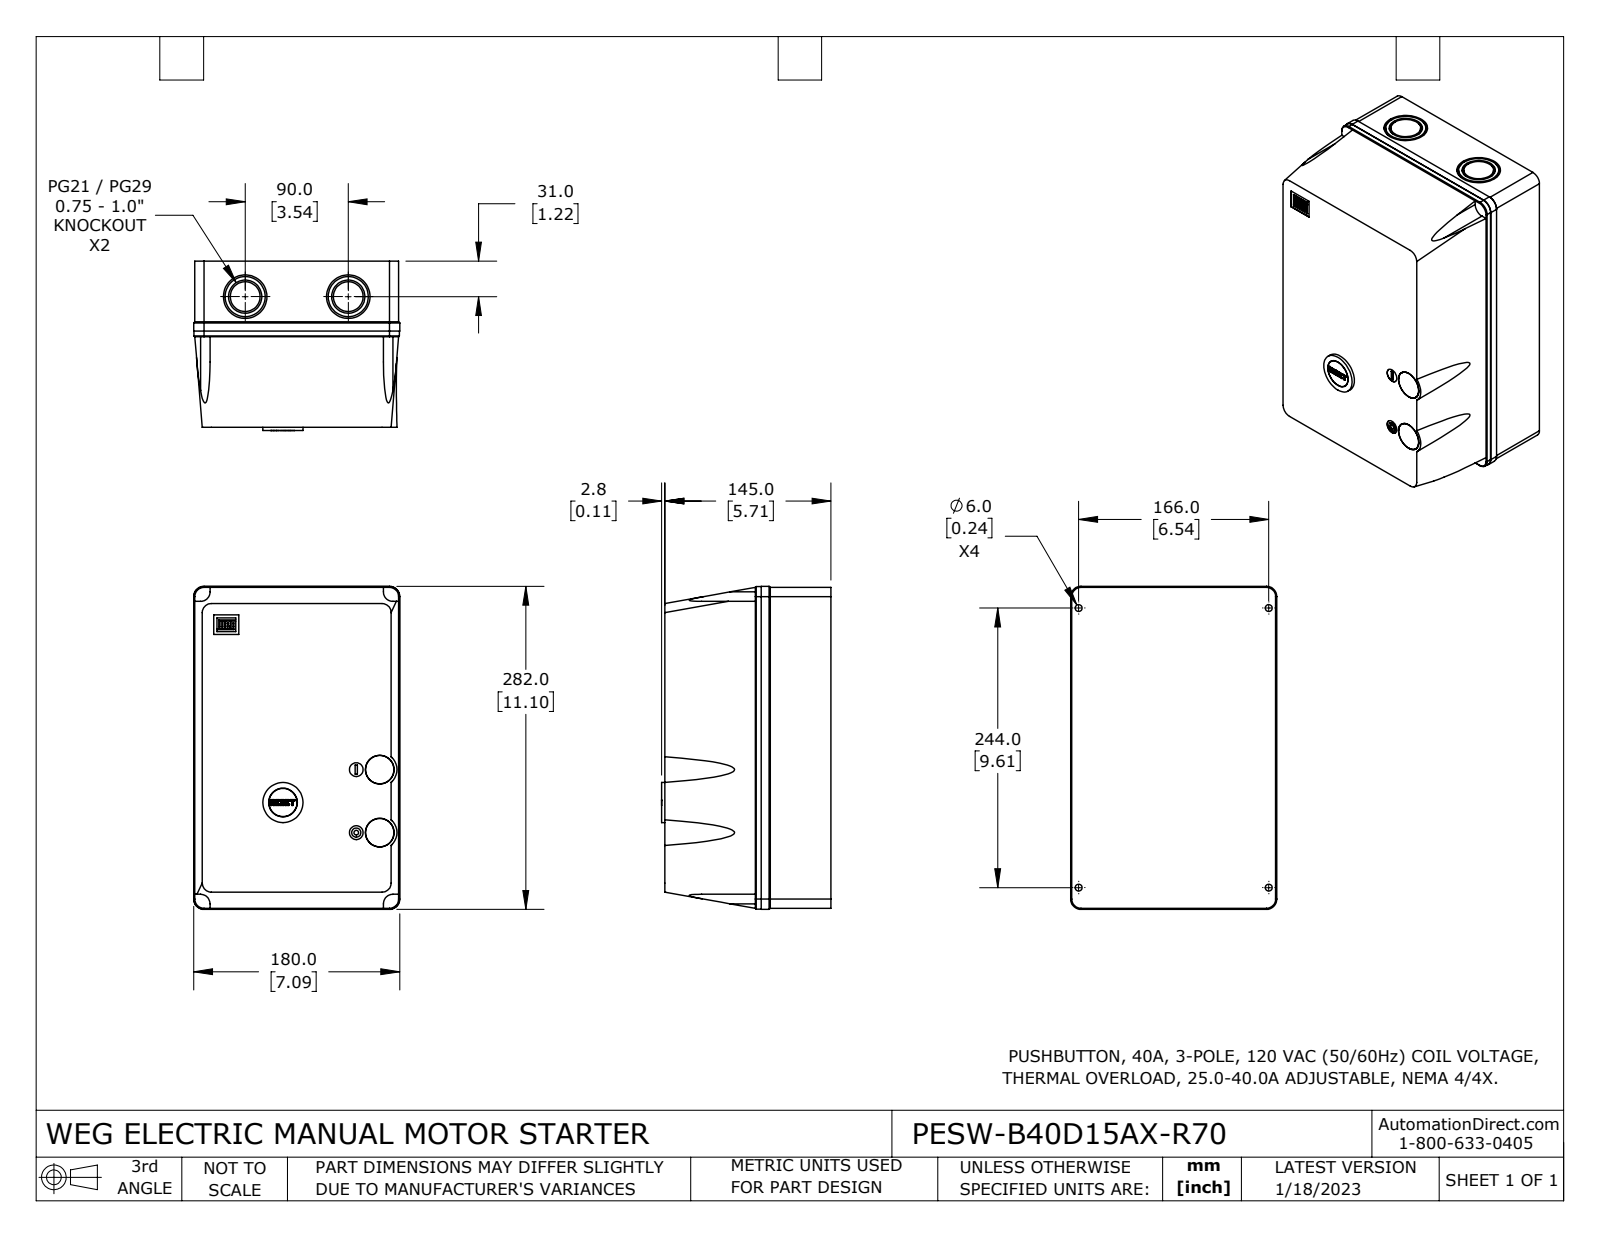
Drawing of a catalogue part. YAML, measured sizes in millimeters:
part_name: "PESW-B40D15AX-R70"
step_written_by: "SolidWorks 2021 (CONFIG_CONTROL_DESIGN)"
units: millimeters
bodies: {solids: 3, faces: 286, planar: 130, cylindrical: 144, other: 12}
overall_size: [282, 180, 147.9]
volume: 7014000
surface_area: 232257
round_holes:
  - {diameter: 6, count: 4}
  - {diameter: 25, count: 3}
  - {diameter: 12, count: 2}
  - {diameter: 29, count: 2}
  - {diameter: 38, count: 2}
  - {diameter: 4, count: 1}
  - {diameter: 30.5, count: 1}
round_bosses_or_shafts:
  - {diameter: 35, count: 3}
  - {diameter: 26, count: 2}
  - {diameter: 24.8, count: 2}
  - {diameter: 30.3, count: 1}
  - {diameter: 24.6, count: 1}
  - {diameter: 14, count: 1}
  - {diameter: 8, count: 1}
partial_cylinders:
  - {radius: 0.1, count: 34}
  - {radius: 8, count: 4}
  - {radius: 8.3, count: 4}
  - {radius: 8.7, count: 4}
  - {radius: 9, count: 4}
  - {radius: 1.6, count: 1}
face_to_face_distances: [145, 178, 280, 1, 0.7, 179, 179.7, 178.7, 281, 180]
hole_center_spacings: [20.5, 55, 58.7, 166, 244, 295.11, 49.14, 57.14]
